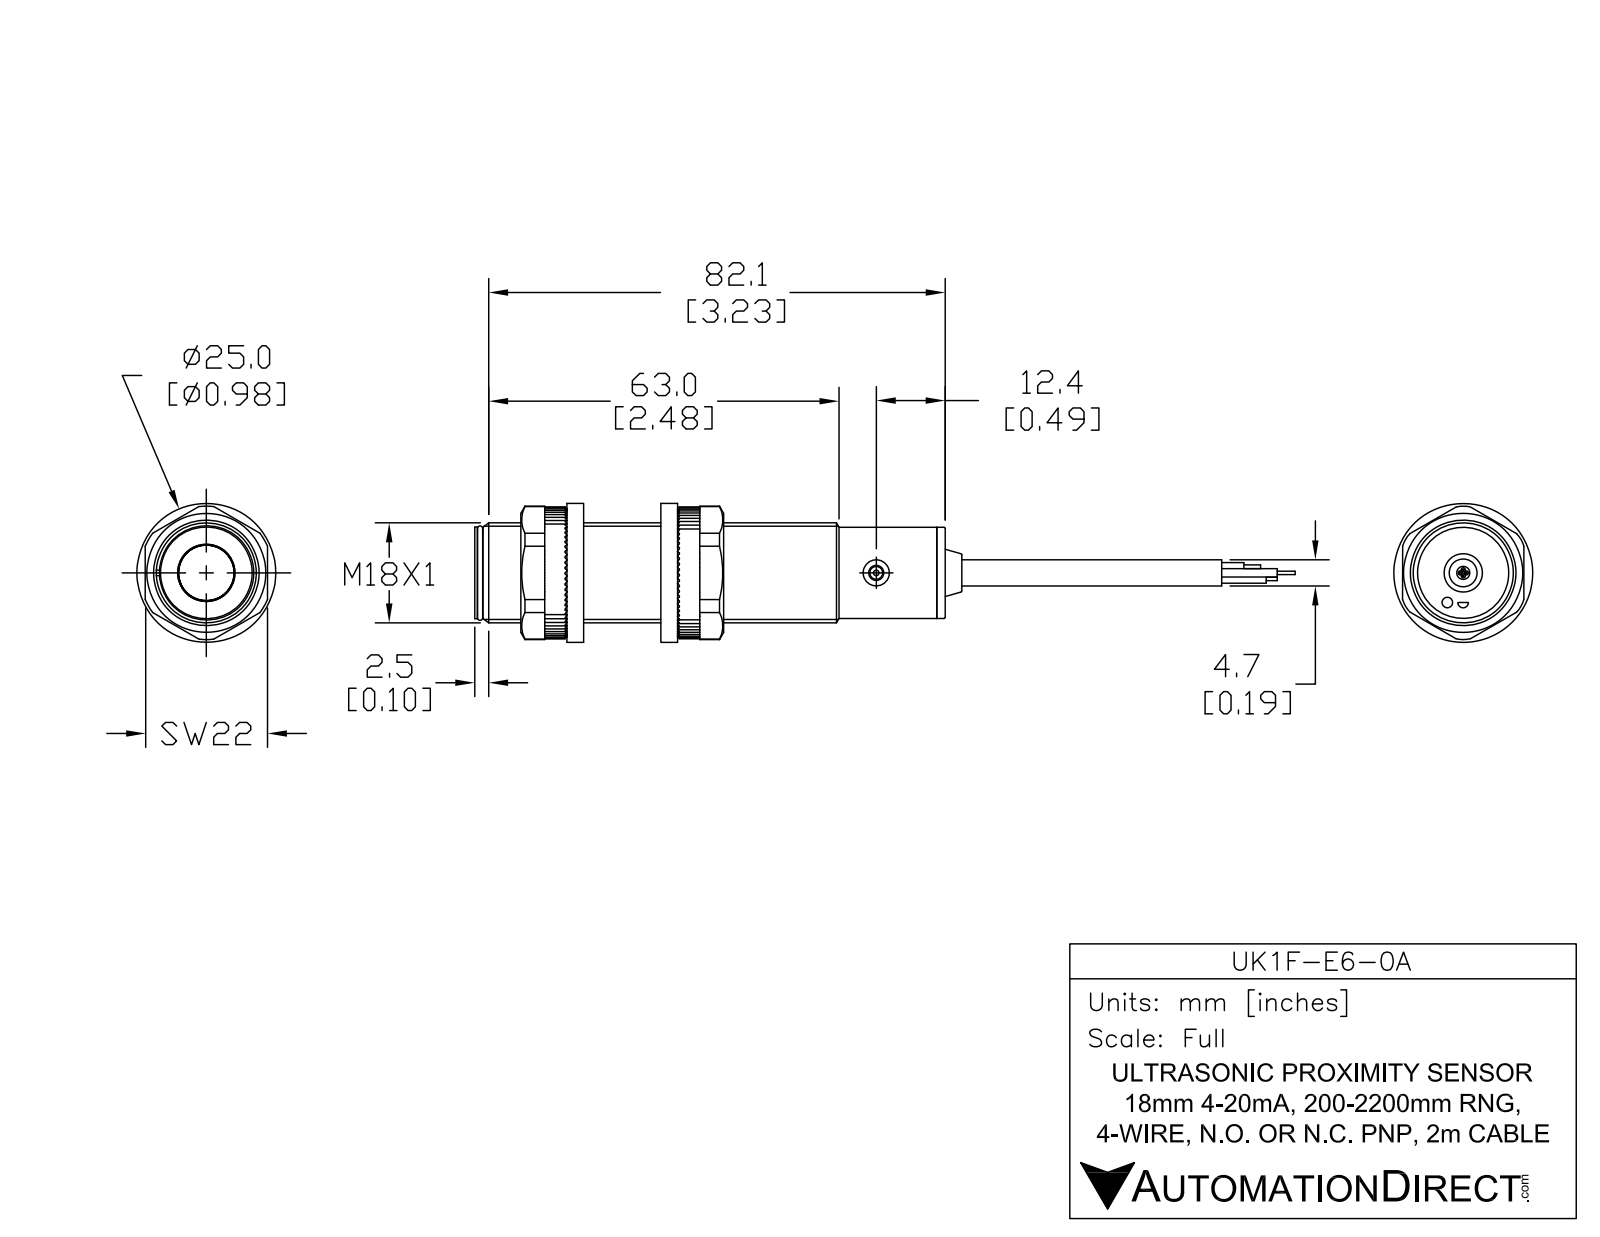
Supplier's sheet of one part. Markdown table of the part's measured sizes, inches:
| quantity | value |
| --- | --- |
| part name | UK1F-E6-0A |
| STEP written by | SolidWorks 2017 (AUTOMOTIVE_DESIGN) |
| units | inches |
| bodies | 6 solids, 55 faces (17 planar, 24 cylindrical, 14 other) |
| overall size | 4.832 × 0.709 × 0.709 |
| volume | 1.285 in³ |
| surface area | 10.69 in² |
| round holes (diameter × count) | 0.185 × 2, 0.106 × 1 |
| round bosses / shafts (diameter × count) | 0.709 × 1, 0.646 × 1, 0.622 × 1, 0.374 × 1, 0.189 × 1, 0.091 × 1 |
| main face-to-face distances | 3.193, 3.252, 0.059, 0.039, 3.232, 3.291, 0.041, 3.234, 3.293, 3.257 |
